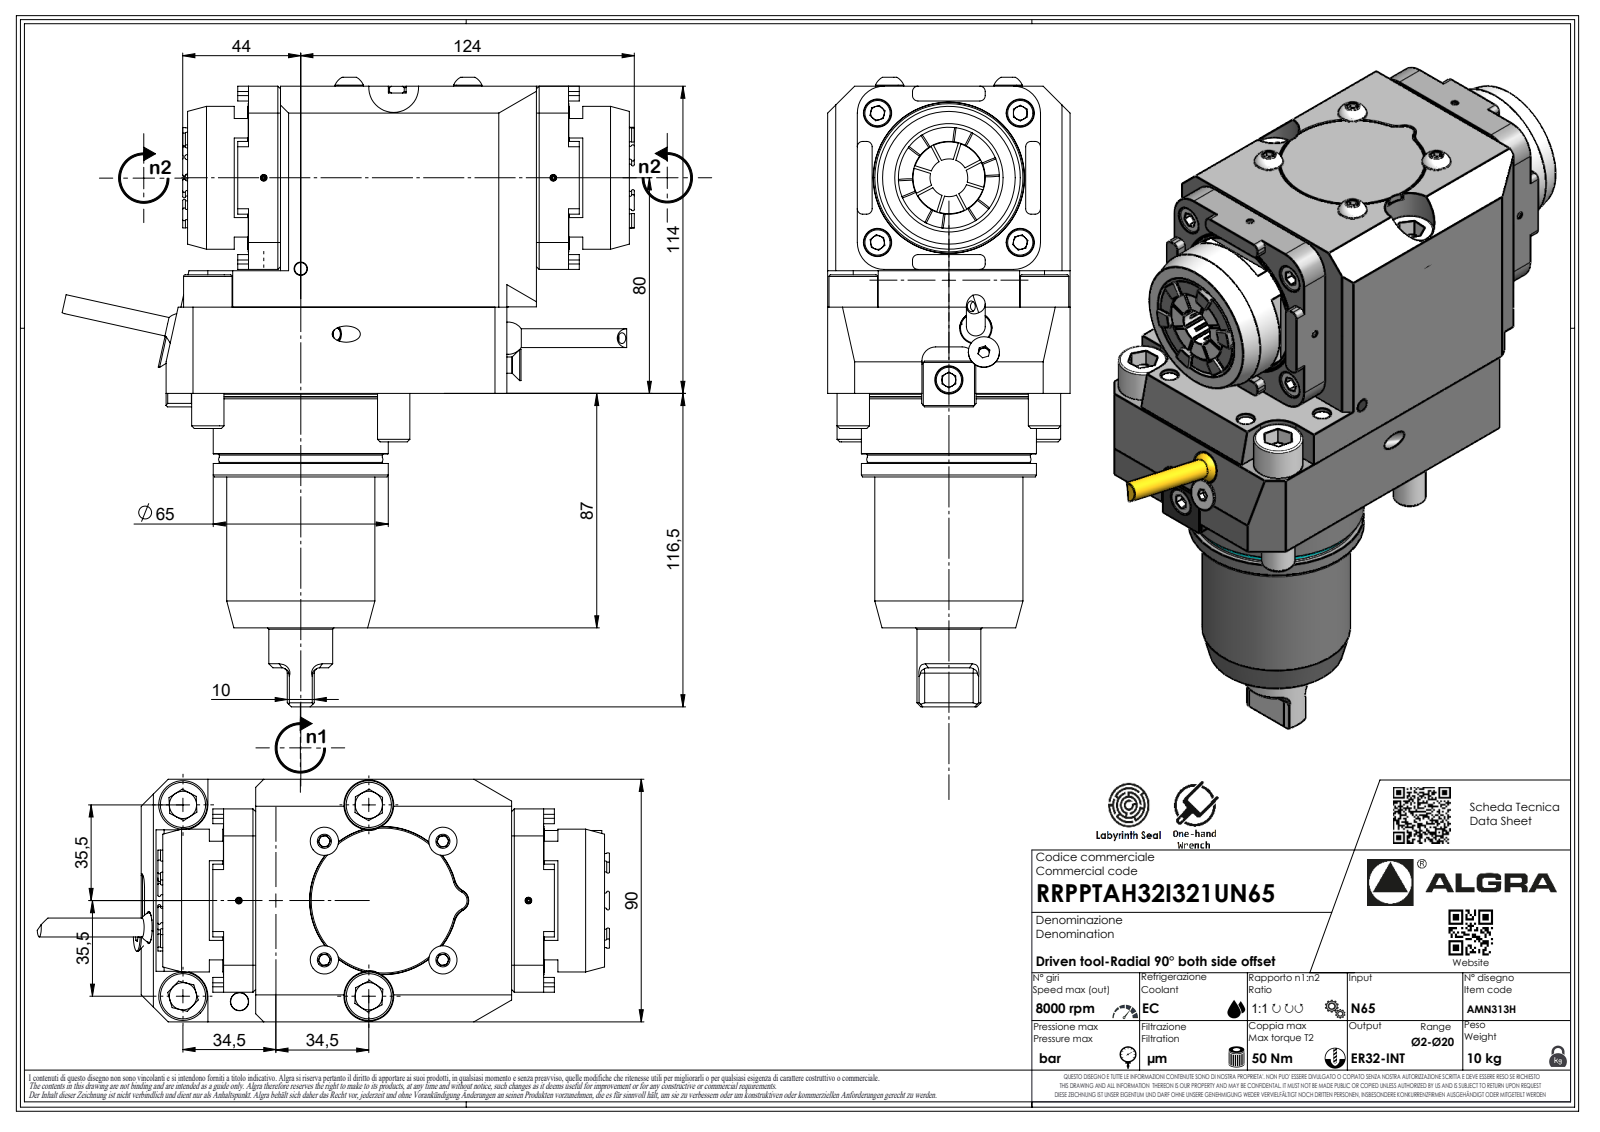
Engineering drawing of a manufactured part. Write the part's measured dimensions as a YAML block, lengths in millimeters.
part_name: "RRPPTAH32I321UN65"
step_written_by: "SolidWorks 2023 (AUTOMOTIVE_DESIGN)"
units: millimeters
bodies: {solids: 1, faces: 594, planar: 373, cylindrical: 99, other: 122}
overall_size: [230.3, 210.59, 90]
volume: 1540000
surface_area: 106107
round_holes:
  - {diameter: 4, count: 2}
  - {diameter: 2.1, count: 1}
round_bosses_or_shafts:
  - {diameter: 12, count: 4}
  - {diameter: 18, count: 2}
  - {diameter: 7, count: 2}
  - {diameter: 65, count: 1}
  - {diameter: 64.6, count: 1}
  - {diameter: 60.5, count: 1}
  - {diameter: 55, count: 1}
  - {diameter: 53, count: 1}
partial_cylinders:
  - {radius: 2, count: 23}
  - {radius: 0.33, count: 7}
  - {radius: 0.52, count: 7}
  - {radius: 3.7, count: 7}
  - {radius: 10, count: 4}
  - {radius: 9.25, count: 3}
  - {radius: 0.21, count: 1}
  - {radius: 4, count: 1}
face_to_face_distances: [90, 114, 45.5, 11, 11.9, 22.6, 141.4, 68, 68.5, 34.5]
